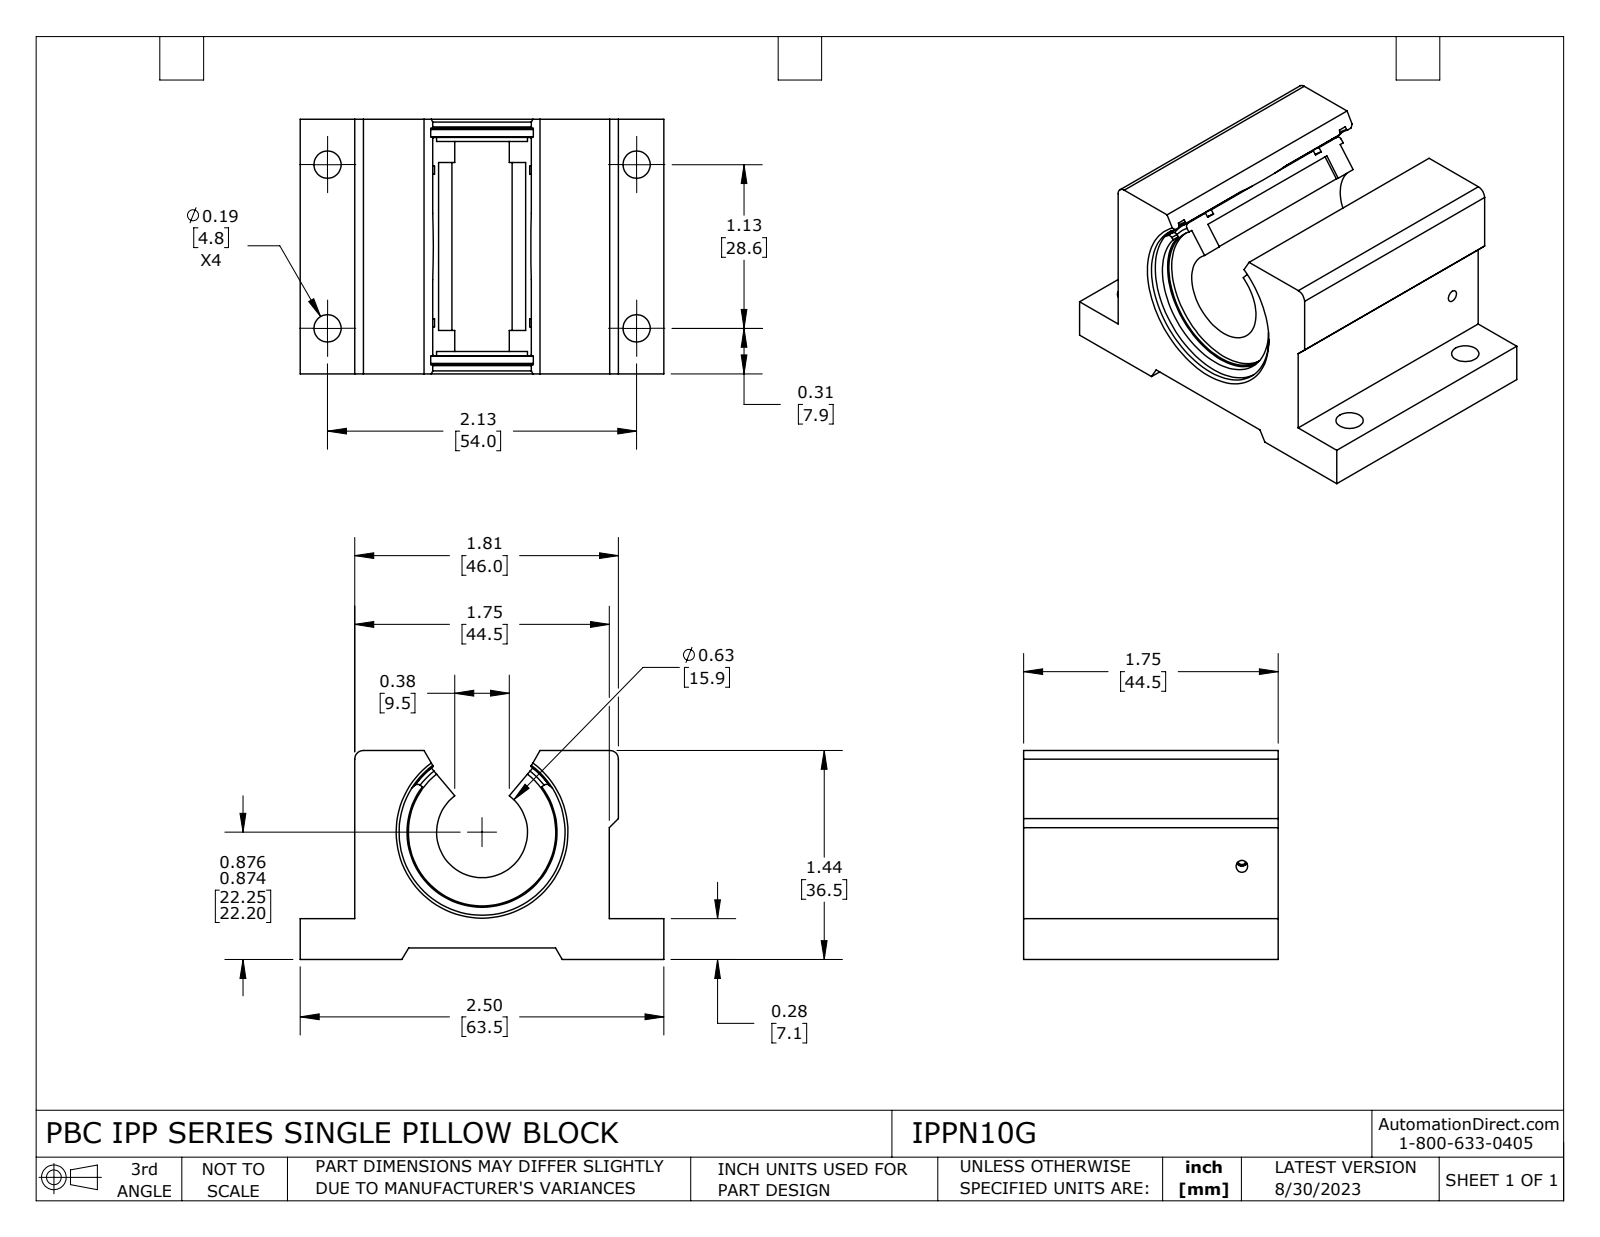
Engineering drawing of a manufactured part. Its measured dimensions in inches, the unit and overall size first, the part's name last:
Units: inches
Overall size (bounding box): 2.5 × 1.75 × 1.437
Round holes (diameter × count): ⌀0.187 ×4, ⌀0.054 ×1, ⌀0.079 ×1, ⌀0.105 ×1, ⌀0.625 ×1, ⌀1.141 ×1, ⌀1.197 ×1
Round bosses / shafts (diameter × count): ⌀0.078 ×1
Partial cylindrical surfaces — rounded edges, fillets, slot ends (radius × count): R0.03 ×2, R0.06 ×2, R0.18 ×2, R0.486 ×1, R0.507 ×1, R0.516 ×1, R0.529 ×1, R0.562 ×1
Main face-to-face distances: 1.75, 0.08, 1.437, 1.357, 0.281, 0.201, 1.156, 0.375, 2.125, 0.153
Hole centre spacings: 1.125, 2.125, 2.405
Volume: 3.599 in³ · Surface area: 32.25 in²
Bodies: 5 solids, 157 faces (52 planar, 74 cylindrical, 31 other)
Part name (STEP PRODUCT): IPPN10G
STEP written by: SolidWorks 2021 (CONFIG_CONTROL_DESIGN)
